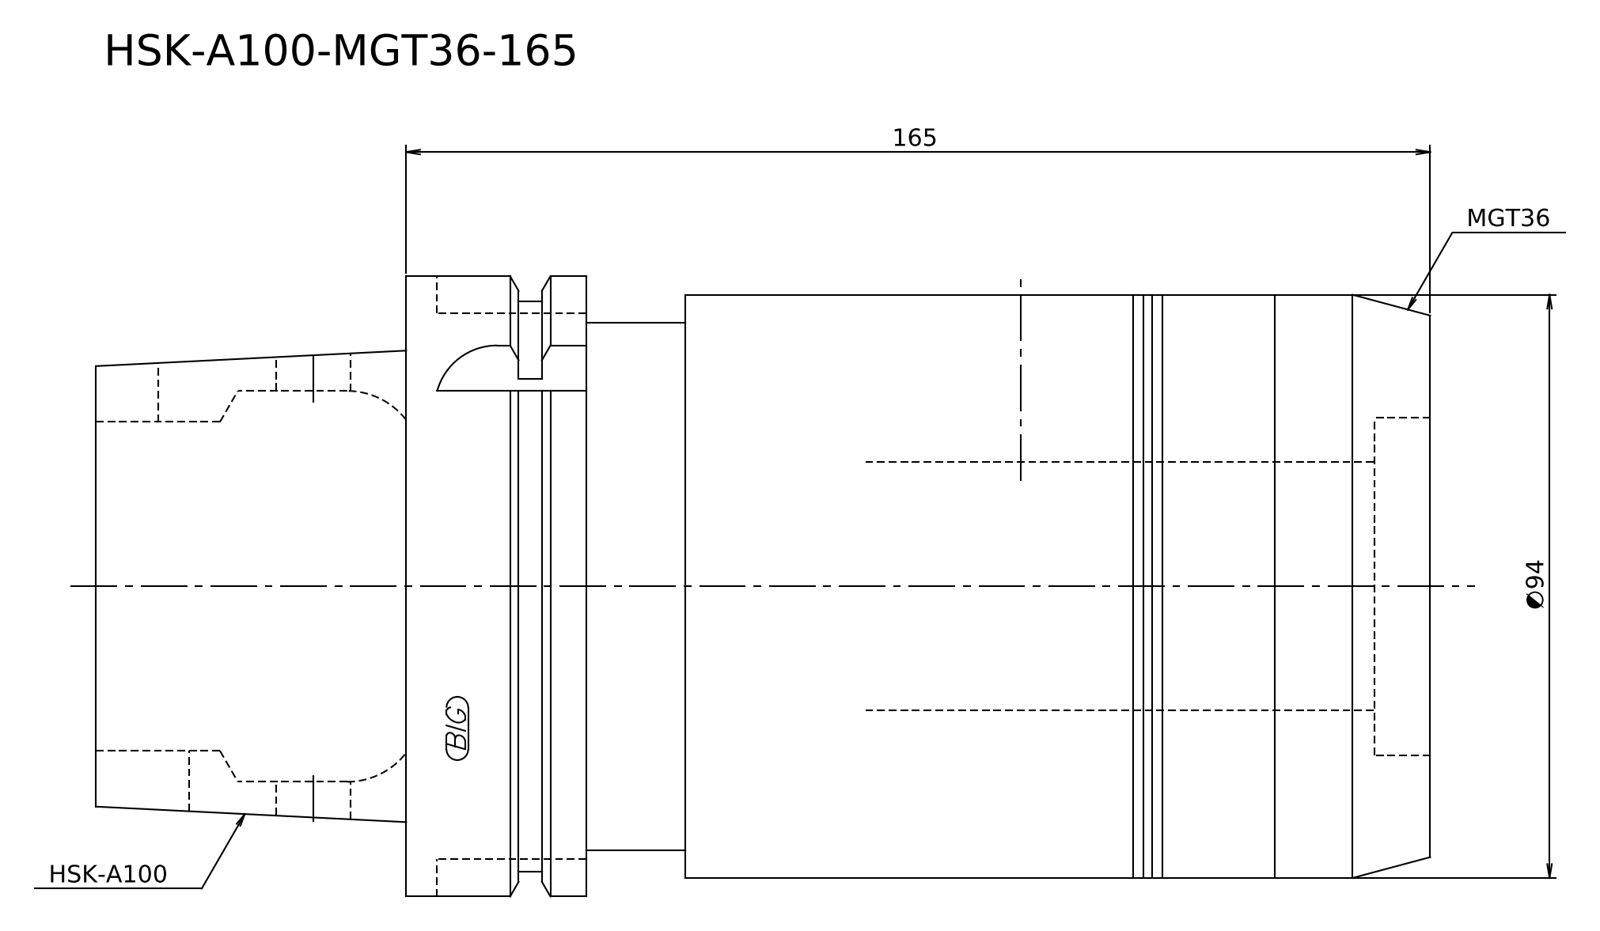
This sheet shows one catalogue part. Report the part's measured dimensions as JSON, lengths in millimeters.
{"step_written_by": "Kubotek KeyCreator V8.5.1 (14335) (CONFIG_CONTROL_DESIGN)", "units": "millimeters", "bodies": {"solids": 1, "faces": 17, "planar": 7, "cylindrical": 6, "other": 4}, "overall_size": [215, 100, 100], "volume_mm3": 1352000, "surface_area_mm2": 78786, "round_bosses_or_shafts": [[100, 1], [94, 1], [92, 1], [85, 1], [75.8, 1]], "face_to_face_distances": [215, 165, 50, 136, 29, 79, 120, 16, 45, 95]}
